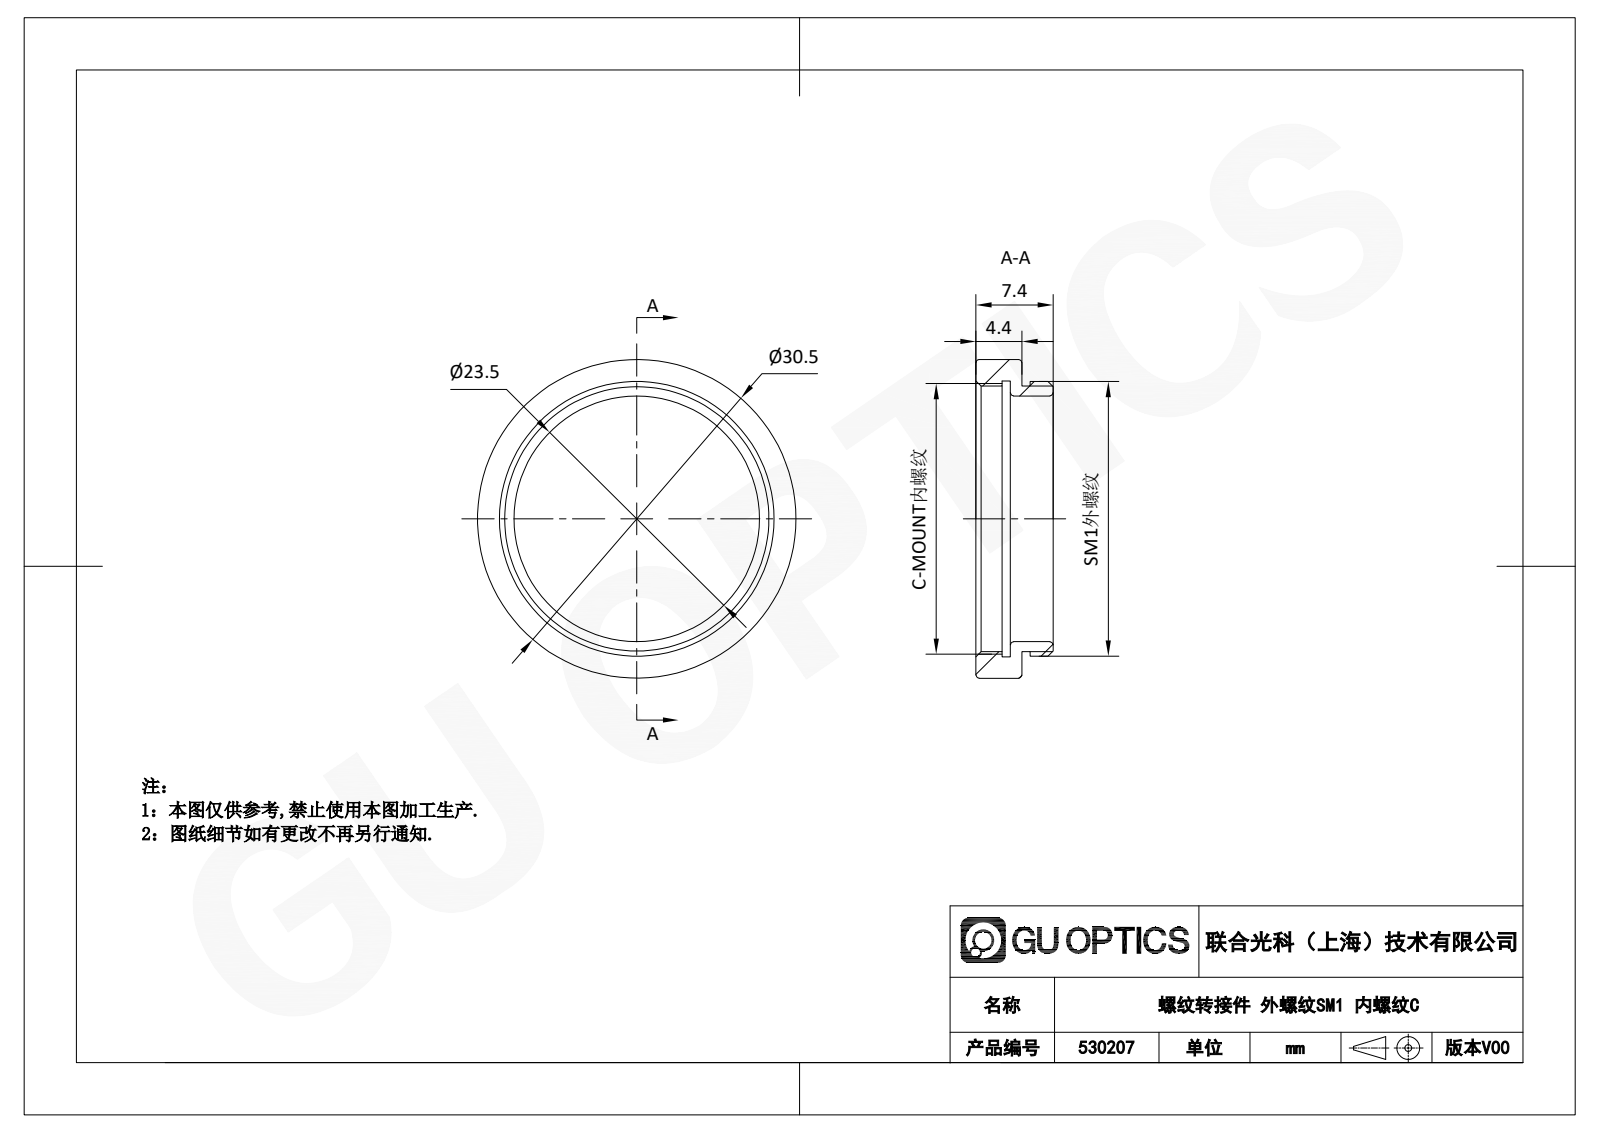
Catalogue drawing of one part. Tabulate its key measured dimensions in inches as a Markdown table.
| quantity | value |
| --- | --- |
| part name | 530207 |
| STEP written by | SolidWorks 2020 (CONFIG_CONTROL_DESIGN) |
| units | inches |
| bodies | 1 solid, 18 faces (6 planar, 6 cylindrical, 6 other) |
| overall size | 1.201 × 1.201 × 0.291 |
| volume | 0.08 in³ |
| surface area | 2.931 in² |
| round holes (diameter × count) | 0.925 × 1, 1 × 1, 1.039 × 1 |
| round bosses / shafts (diameter × count) | 1.201 × 1, 1.035 × 1 |
| main face-to-face distances | 0.173, 0.043, 0.13, 0.031, 0.075, 0.118, 0.161, 0.291, 0.193, 0.098 |
